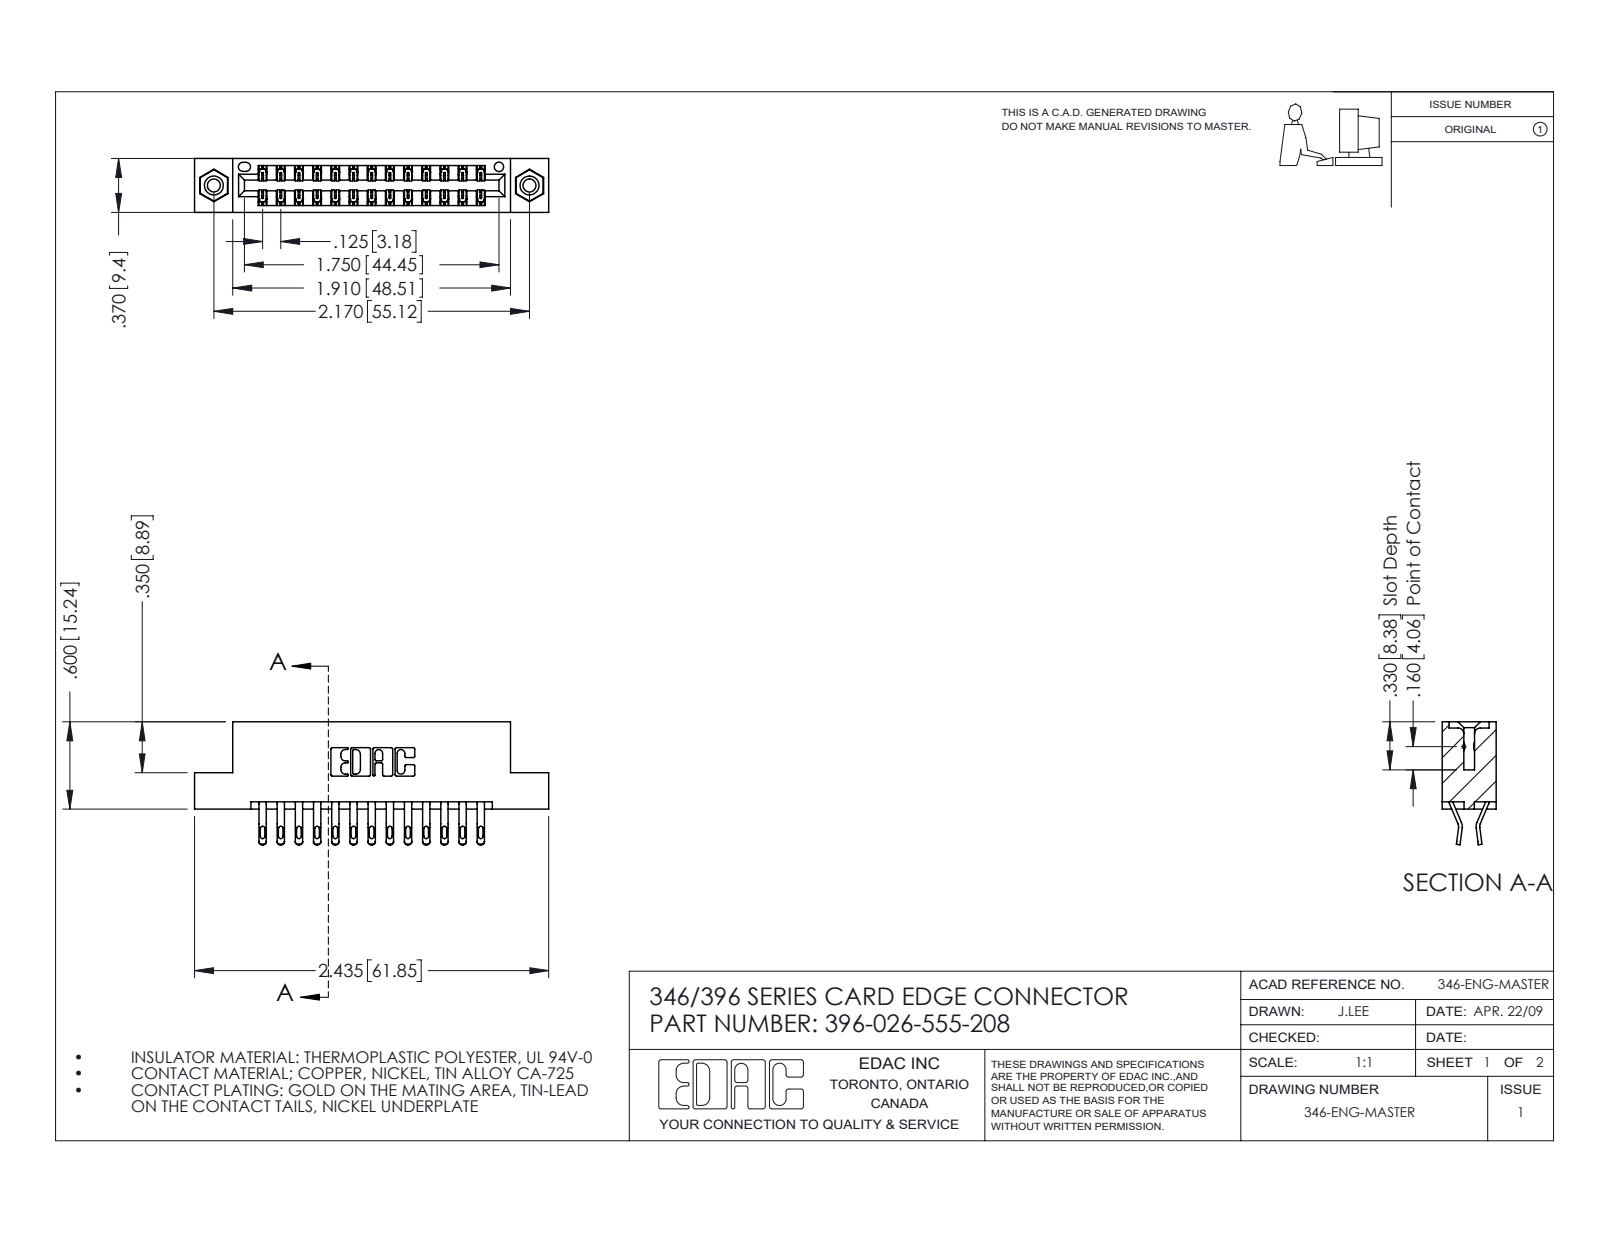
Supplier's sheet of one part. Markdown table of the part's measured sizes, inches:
| quantity | value |
| --- | --- |
| part name | 346 Part_Flush Mounting Lugs - 0.156 Dia-TI; 396-026-555-208; 345-292-001_555 Tail; 345-250-001_345-250-003-102 |
| STEP written by | SolidWorks 2016 (CONFIG_CONTROL_DESIGN) |
| units | inches |
| bodies | 29 solids, 1690 faces (966 planar, 708 cylindrical, 16 other) |
| overall size | 2.435 × 0.845 × 0.37 |
| volume | 0.358 in³ |
| surface area | 12.26 in² |
| round holes (diameter × count) | 0.089 × 2, 0.125 × 2, 0.156 × 2, 0.064 × 1 |
| round bosses / shafts (diameter × count) | 0.155 × 2 |
| partial cylindrical surfaces (radius × count) | 0.016 × 52, 0.02 × 52, 0.006 × 39, 0.01 × 22, 0.007 × 6, 0.031 × 6, 0.026 × 3, 0.01 × 2 |
| main face-to-face distances | 0.25, 0.048, 0.322, 0.37, 0.025, 0.072, 0.298, 0.275, 0.148, 0.222 |
| hole center spacings | 0.246, 1.964, 2.17 |
